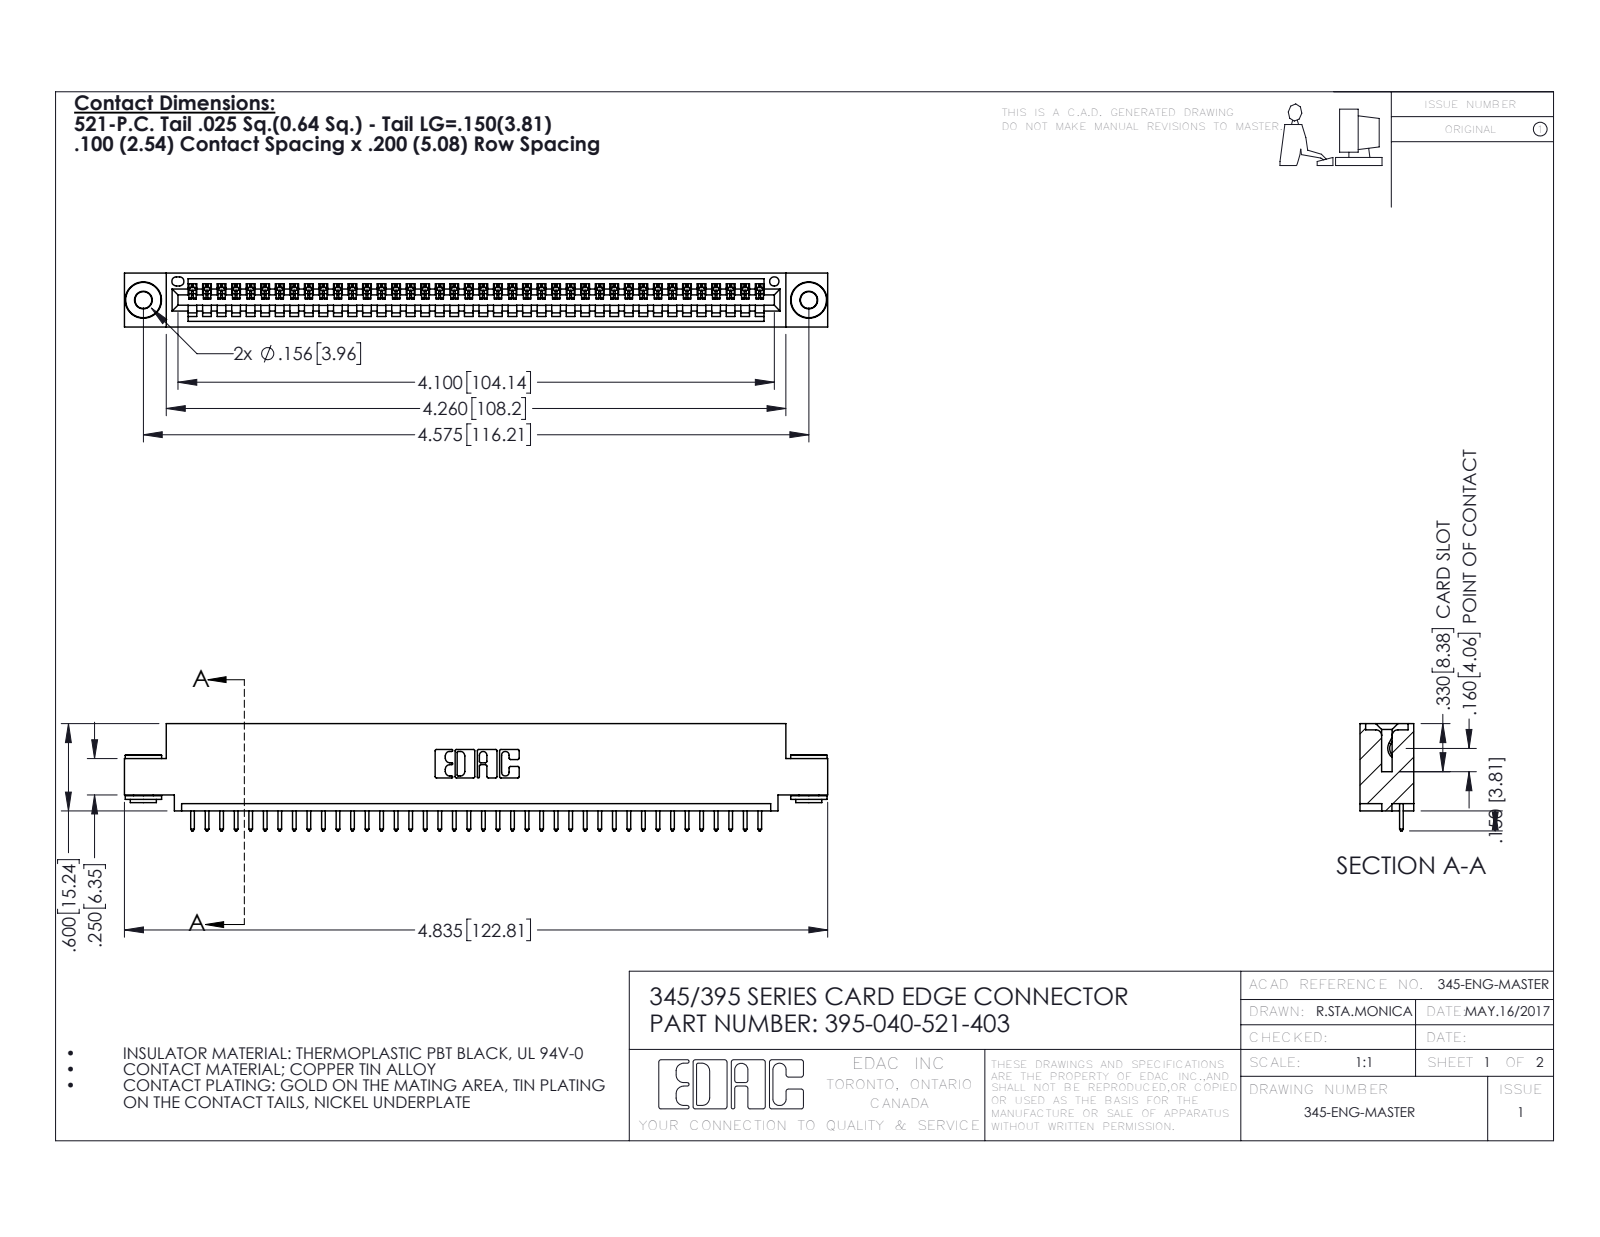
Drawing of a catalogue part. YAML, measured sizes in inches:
part_name: "345-292-001_345-293-121; 345 Part_0.110 Offset - 0.156 Dia-TH; 395-040-521-403; 345-250-002_345-250-002-102"
step_written_by: "SolidWorks 2016 (CONFIG_CONTROL_DESIGN)"
units: inches
bodies: {solids: 43, faces: 2488, planar: 1694, cylindrical: 786, other: 8}
overall_size: [4.835, 0.737, 0.37]
volume: 0.701
surface_area: 23.37
round_holes:
  - {diameter: 0.116, count: 2}
  - {diameter: 0.156, count: 2}
  - {diameter: 0.064, count: 1}
round_bosses_or_shafts:
  - {diameter: 0.25, count: 2}
  - {diameter: 0.18, count: 2}
  - {diameter: 0.136, count: 2}
partial_cylinders:
  - {radius: 0.006, count: 80}
  - {radius: 0.01, count: 80}
  - {radius: 0.01, count: 22}
  - {radius: 0.007, count: 6}
  - {radius: 0.031, count: 6}
  - {radius: 0.026, count: 3}
  - {radius: 0.031, count: 2}
  - {radius: 0.04, count: 2}
face_to_face_distances: [0.072, 0.298, 0.37, 0.2, 0.025, 0.098, 0.272, 0.225, 0.149, 0.072]
hole_center_spacings: [0.27, 4.339, 4.575]
